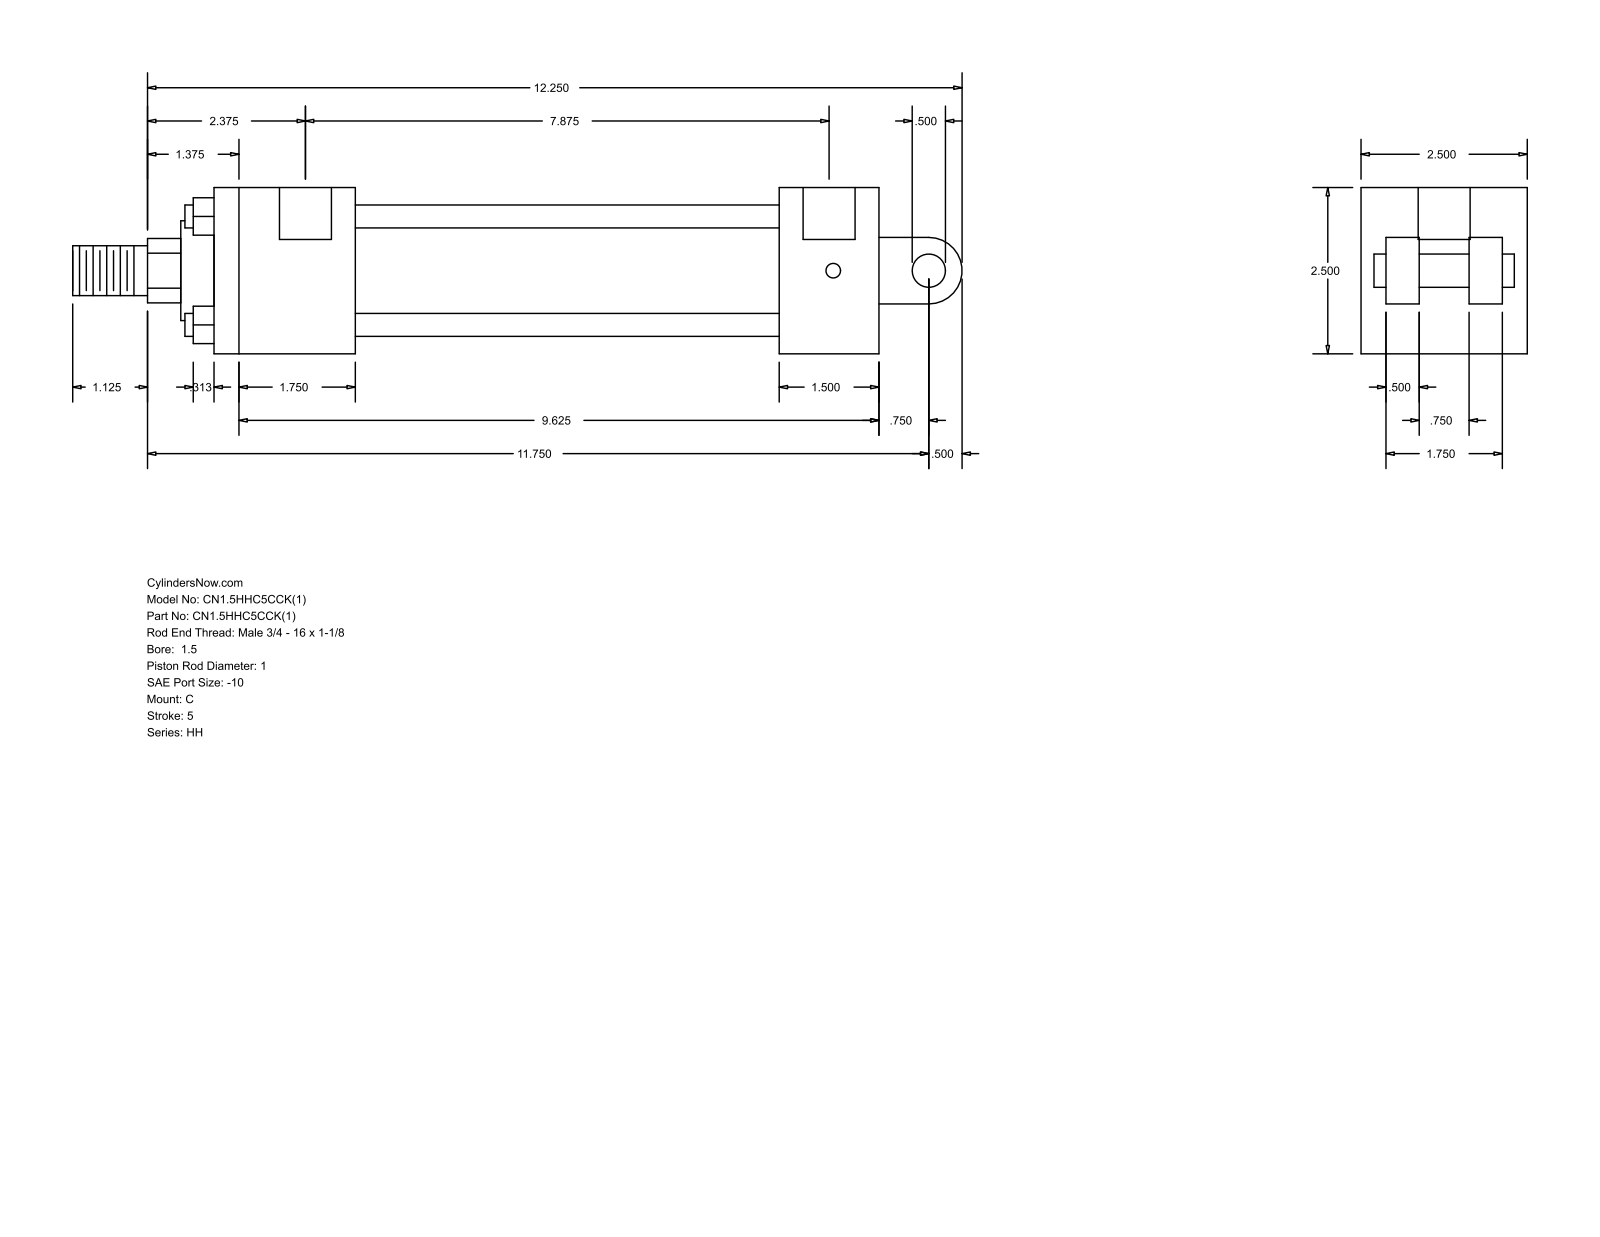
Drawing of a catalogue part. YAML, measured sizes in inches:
part_name: "HH_C__0150_1"
step_written_by: "GSSL Pune (CONFIG_CONTROL_DESIGN)"
units: inches
bodies: {solids: 0, faces: 99, planar: 70, cylindrical: 29, other: 0}
overall_size: [13.375, 2.5, 2.5]
round_holes:
  - {diameter: 0.219, count: 4}
  - {diameter: 0.781, count: 2}
round_bosses_or_shafts:
  - {diameter: 0.345, count: 4}
  - {diameter: 1.75, count: 1}
  - {diameter: 1.5, count: 1}
  - {diameter: 1, count: 1}
  - {diameter: 0.75, count: 1}
  - {diameter: 0.5, count: 1}
partial_cylinders:
  - {radius: 0.484, count: 1}
  - {radius: 0.5, count: 1}
face_to_face_distances: [2.5, 2.125, 1.5, 6.375, 7.875, 8.5, 10, 0.5, 0.875, 1.625]
hole_center_spacings: [0.063, 7.937, 8, 7.875]
